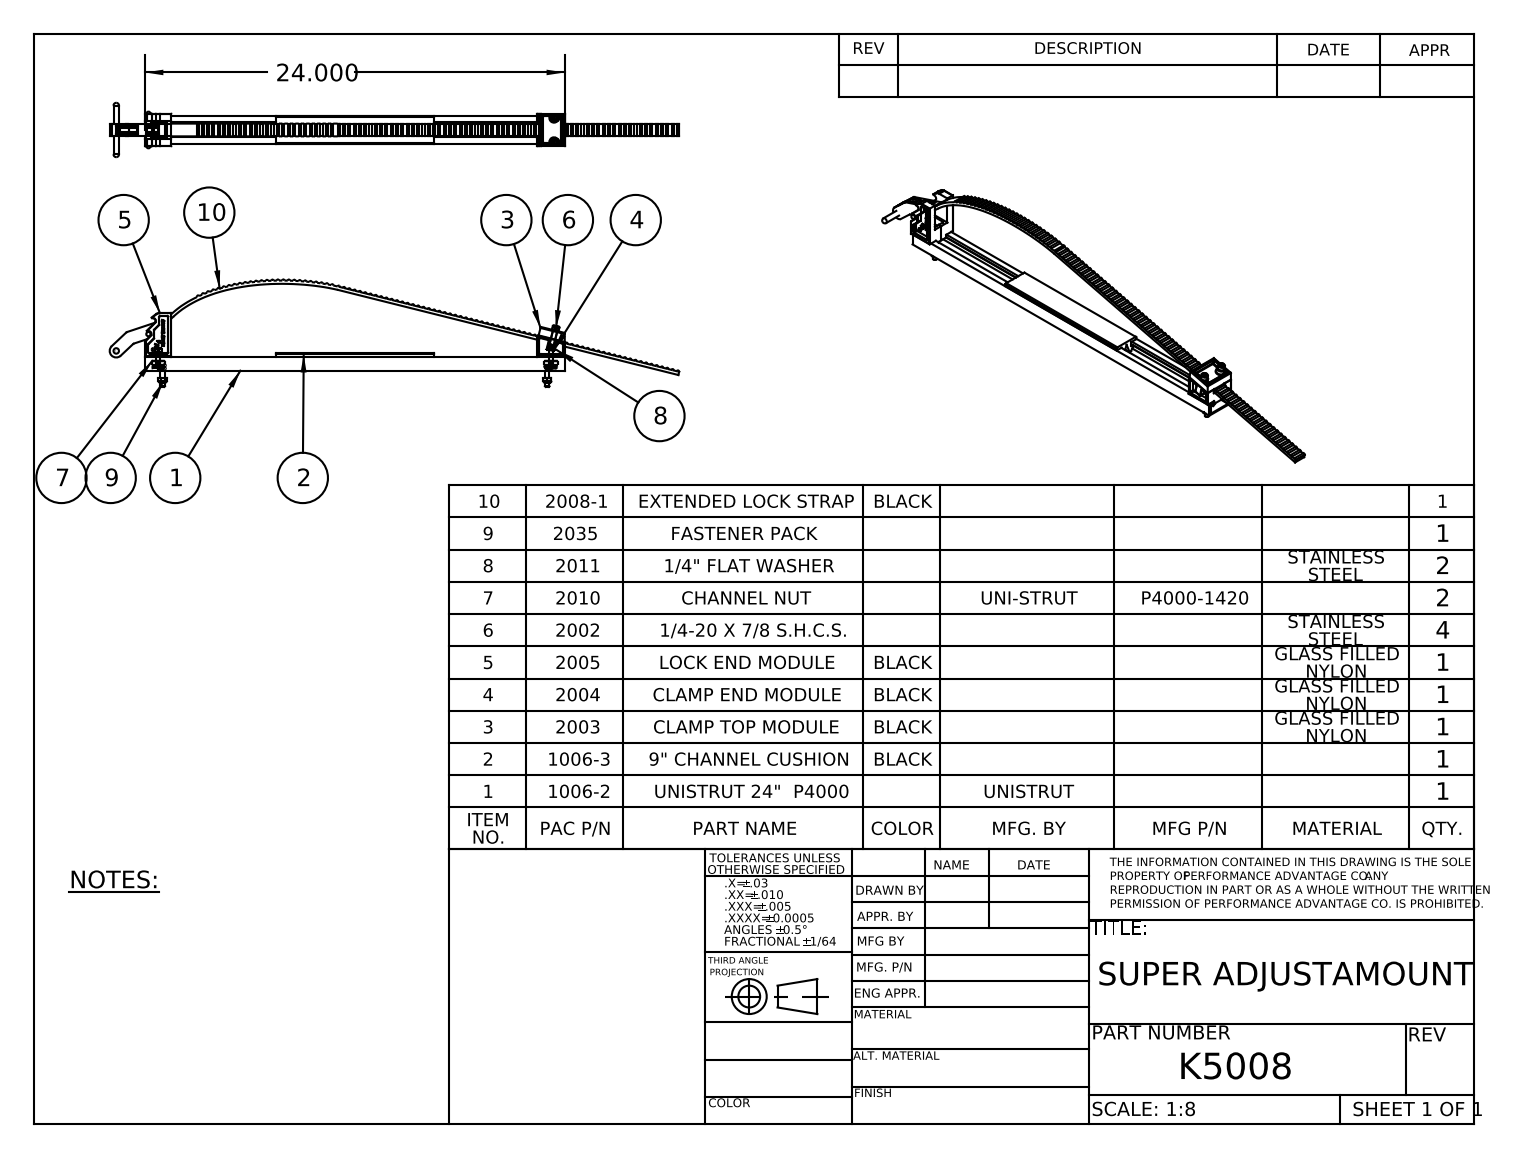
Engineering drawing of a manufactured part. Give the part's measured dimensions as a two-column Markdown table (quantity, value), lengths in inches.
| quantity | value |
| --- | --- |
| part name | K5008; 1006-2; 1006-3; 2003 (+8 more) |
| STEP written by | SolidWorks 2010 (CONFIG_CONTROL_DESIGN) |
| units | inches |
| bodies | 21 solids, 1275 faces (504 planar, 463 cylindrical, 308 other) |
| overall size | 32.573 × 6.141 × 3.106 |
| volume | 28.66 in³ |
| surface area | 403.6 in² |
| round holes (diameter × count) | 0.201 × 6, 0.25 × 4, 0.269 × 2, 0.288 × 2, 0.313 × 2, 0.26 × 1, 0.291 × 1, 0.625 × 1, 0.64 × 1 |
| round bosses / shafts (diameter × count) | 0.25 × 5, 0.375 × 4, 0.404 × 2, 0.625 × 1, 0.313 × 1 |
| partial cylindrical surfaces (radius × count) | 0.063 × 116, 0.062 × 53, 0.031 × 36, 0.02 × 30, 0.06 × 8, 0.25 × 4, 0.424 × 4, 0.156 × 2 |
| main face-to-face distances | 0.078, 0.813, 0.109, 1.516, 0.735, 1.625, 0.448, 1.178, 0.339, 1.069 |
| hole center spacings | 0.214, 0.25, 1.375, 22, 22.214, 22.25, 22.464 |
